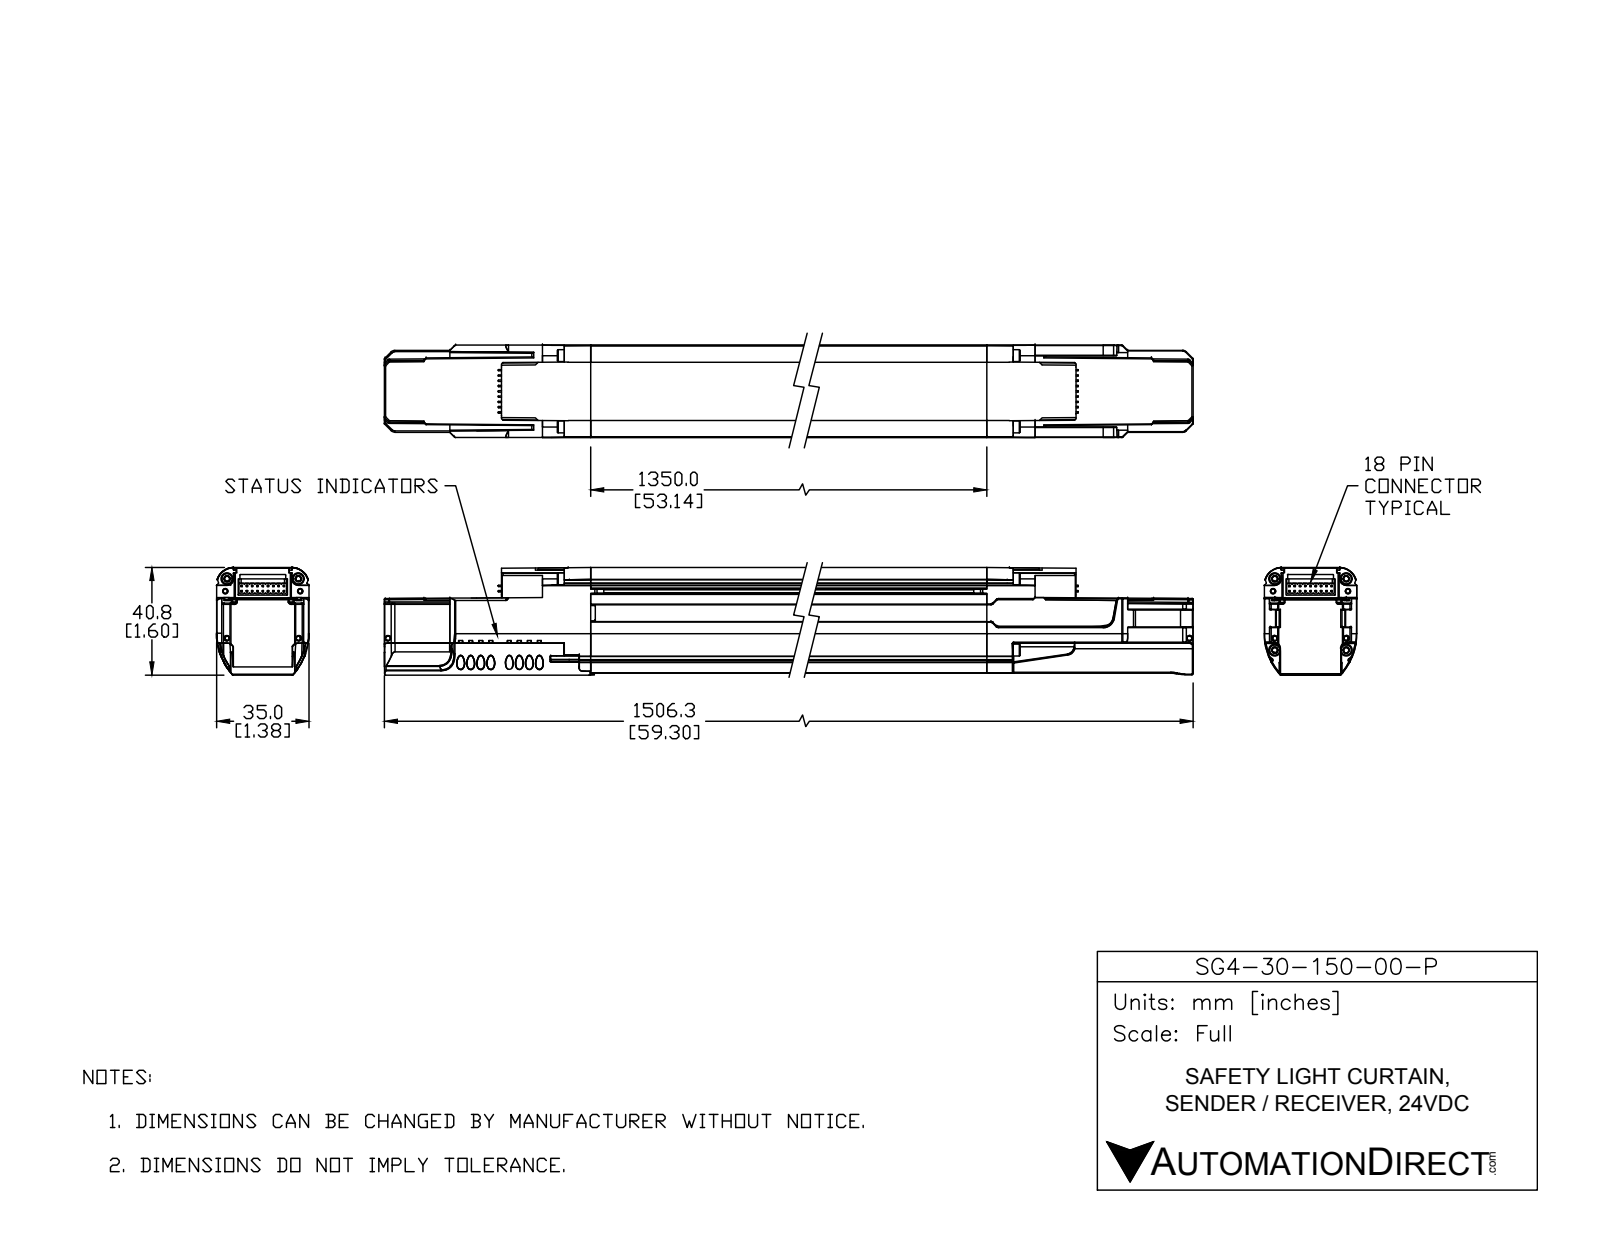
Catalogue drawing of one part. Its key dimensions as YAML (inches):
part_name: "SG4-30-150-OO-P"
step_written_by: "SolidWorks 2017 (AUTOMOTIVE_DESIGN)"
units: inches
bodies: {solids: 16, faces: 534, planar: 362, cylindrical: 110, other: 62}
overall_size: [59.293, 2.58, 2.023]
volume: 113.3
surface_area: 623.8
round_holes:
  - {diameter: 0.07, count: 6}
  - {diameter: 0.1, count: 4}
  - {diameter: 0.165, count: 4}
  - {diameter: 0.209, count: 4}
  - {diameter: 0.26, count: 4}
  - {diameter: 0.065, count: 1}
  - {diameter: 0.065, count: 1}
round_bosses_or_shafts:
  - {diameter: 0.394, count: 4}
  - {diameter: 0.197, count: 4}
partial_cylinders:
  - {radius: 0.106, count: 16}
  - {radius: 0.118, count: 8}
  - {radius: 0.1, count: 4}
  - {radius: 0.11, count: 4}
  - {radius: 0.08, count: 2}
  - {radius: 0.12, count: 2}
  - {radius: 0.123, count: 2}
  - {radius: 0.125, count: 2}
face_to_face_distances: [0.06, 0.084, 0.024, 1.49, 1.466, 1.55, 1.057, 0.481, 0.985, 1.009]
hole_center_spacings: [0.569, 51.565, 0.02, 0.204, 0.207, 0.207, 0.227, 0.71]
